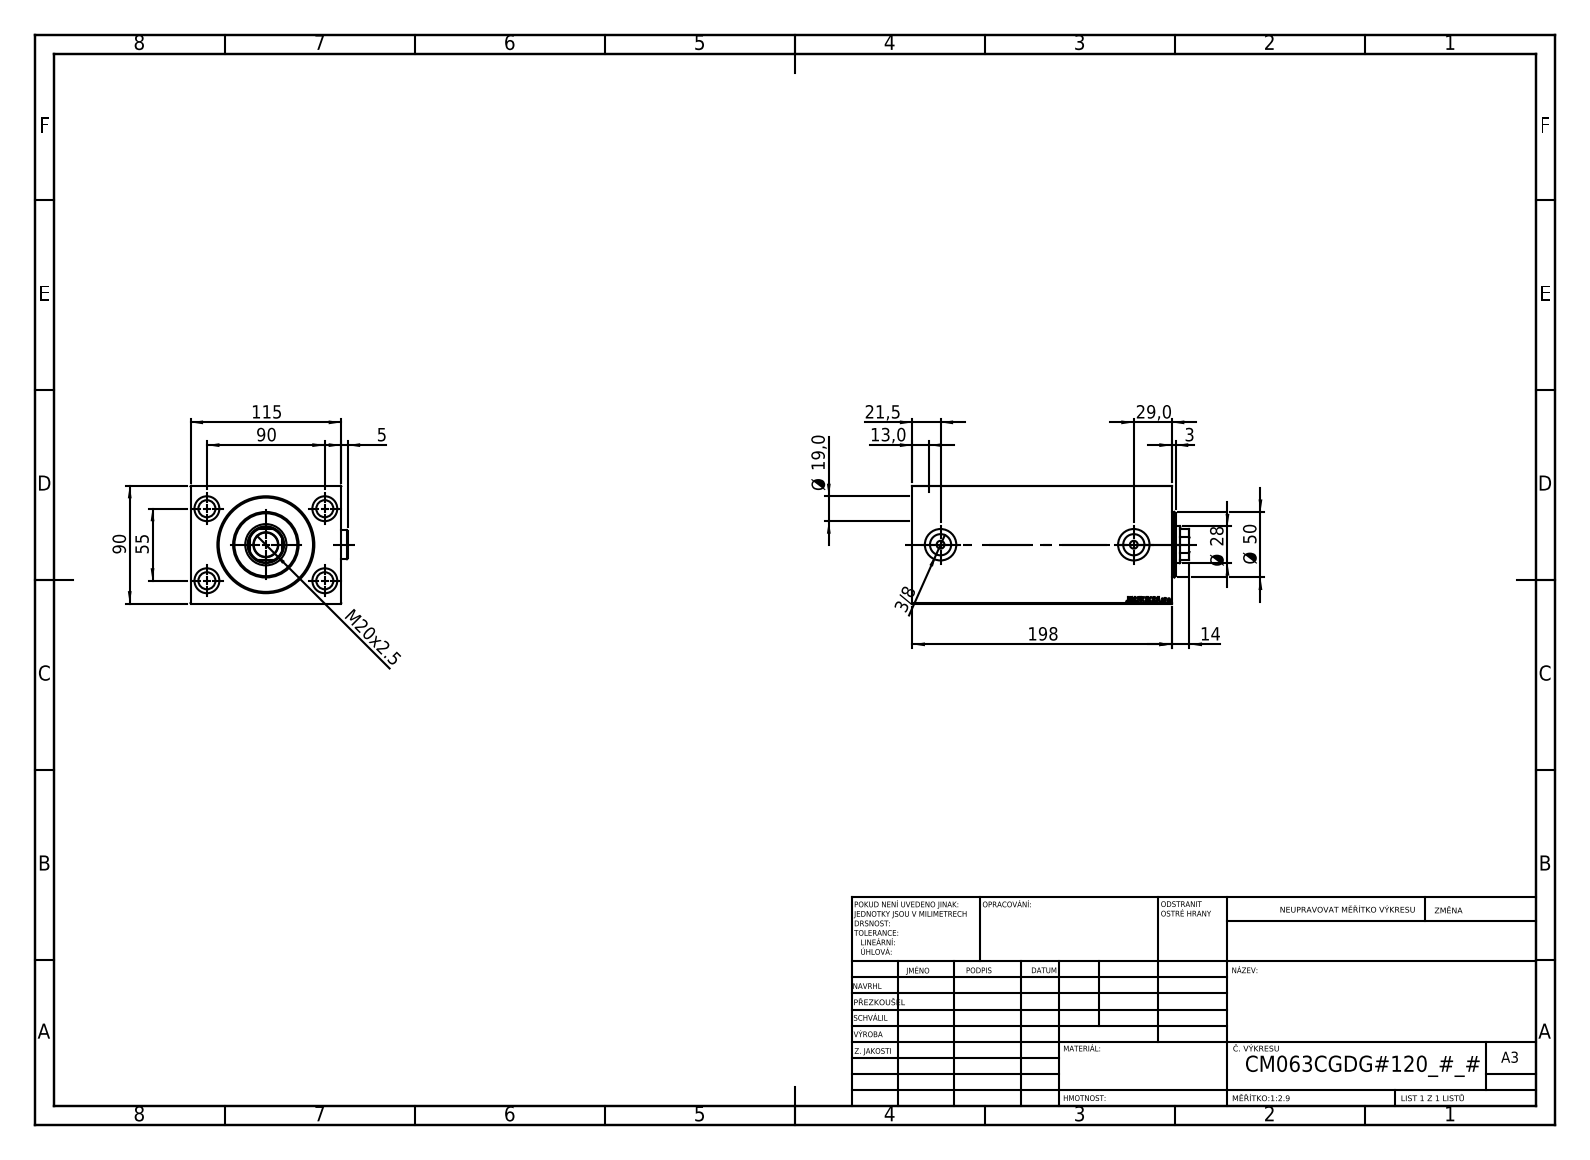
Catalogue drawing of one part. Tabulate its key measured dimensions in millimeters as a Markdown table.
| quantity | value |
| --- | --- |
| part name | V450CM_C_Body; Zatka_OIL_PORT; V450CM_C_VCP; V450CM_VC_B |
| STEP written by | SolidWorks 2019 (CONFIG_CONTROL_DESIGN) |
| units | millimeters |
| bodies | 5 solids, 919 faces (443 planar, 78 cylindrical, 398 other) |
| overall size | 211.5 × 119.9 × 90 |
| volume | 1 623 000 mm³ |
| surface area | 218 078 mm² |
| round holes (diameter × count) | 13 × 4, 19 × 4, 6 × 2, 16.17 × 2, 24 × 2, 18.5 × 1, 28 × 1, 31.5 × 1, 63 × 1, 65 × 1, 72 × 1 |
| round bosses / shafts (diameter × count) | 22 × 2, 50 × 1 |
| partial cylindrical surfaces (radius × count) | 13.5 × 1 |
| main face-to-face distances | 90, 115, 198, 17.5, 180.5, 13.5, 167, 184.5, 64.5, 133.5 |
| hole center spacings | 52.74, 55, 90, 105.48, 147.5 |
